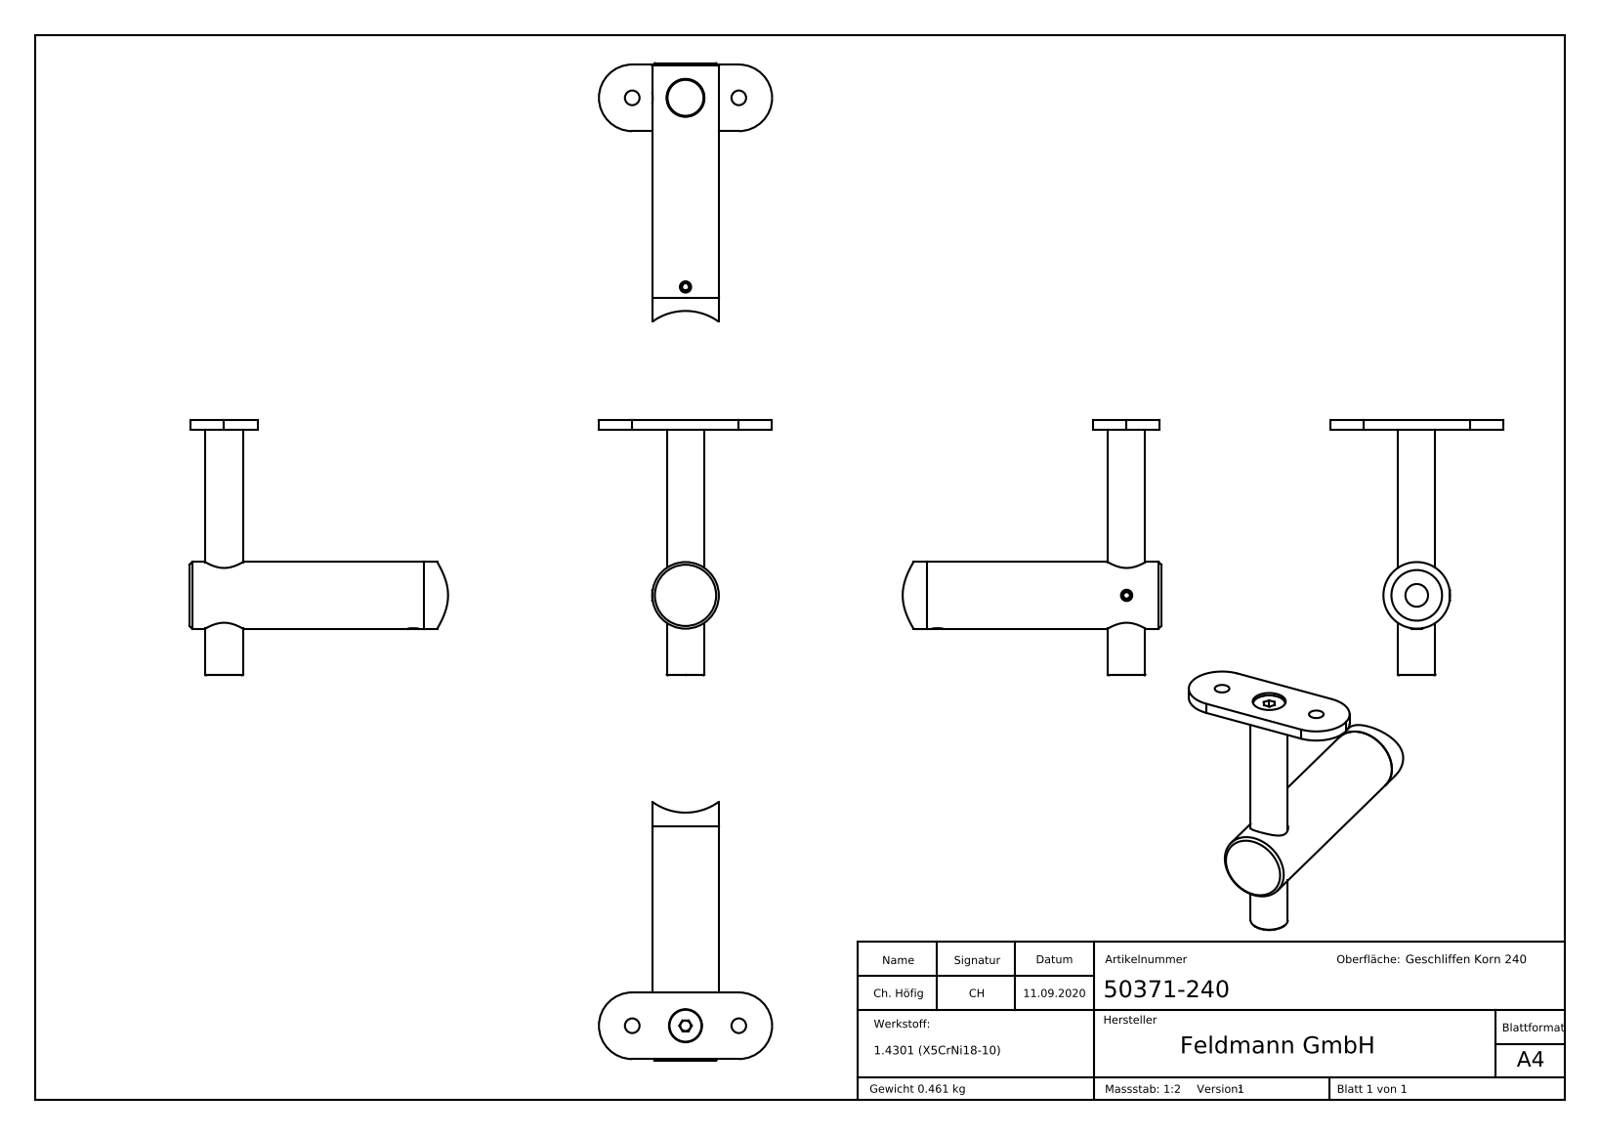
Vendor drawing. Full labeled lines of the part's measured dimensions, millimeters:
Part name (STEP PRODUCT): 50371-240; 5037X-240 Teil2; 5037X-240 Teil4; 5037X-240 Teil2_50371-240 Teil2 (+8 more)
STEP written by: SolidWorks 2018 (CONFIG_CONTROL_DESIGN)
Units: millimetres
Bodies: 7 solids, 348 faces (147 planar, 71 cylindrical, 130 other)
Overall size (bounding box): 97.08 × 96 × 88
Volume: 58 355 mm³ · Surface area: 21 545 mm²
Round holes (diameter × count): ⌀4.2 ×2, ⌀5.5 ×2, ⌀5 ×1, ⌀8 ×1, ⌀8.5 ×1, ⌀12.4 ×1, ⌀14 ×1, ⌀14.2 ×1, ⌀16 ×1, ⌀19 ×1
Round bosses / shafts (diameter × count): ⌀5 ×2, ⌀25 ×1, ⌀12 ×1, ⌀6 ×1
Partial cylindrical surfaces — rounded edges, fillets, slot ends (radius × count): R12.5 ×2, R8.1 ×1, R21.2 ×1
Main face-to-face distances: 4, 88, 0.5, 3, 91, 62.5, 65.5, 90.5, 87.5, 25
Hole centre spacings: 20, 73.76, 40, 71
